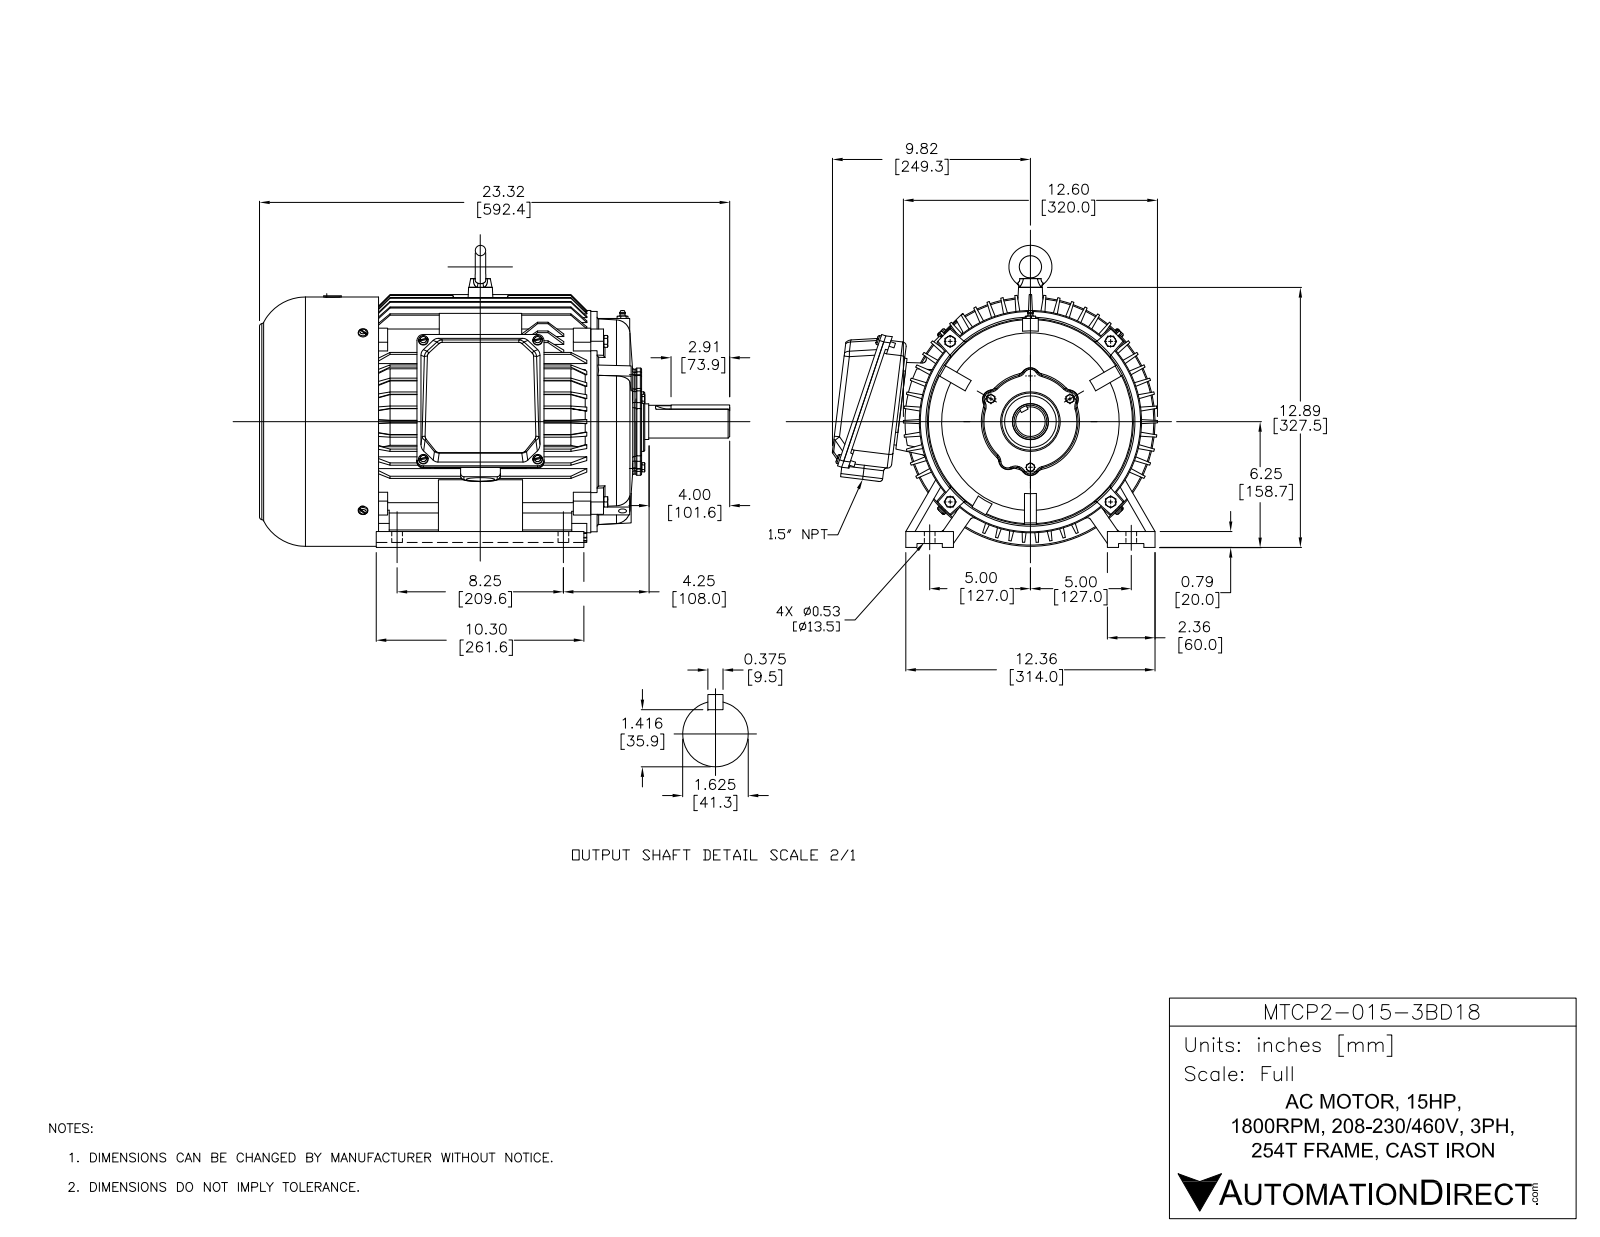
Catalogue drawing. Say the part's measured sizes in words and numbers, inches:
The part is named "PEWWE-254T". Its 3-D file was written by "SolidWorks 2017 (AUTOMOTIVE_DESIGN)". It is 28 solids with 2218 faces: 1376 planar, 420 cylindrical and 422 other. Overall it measures 23.327 by 16.126 by 14.984 inches. Its volume is 453.1 cubic inches and its surface area 3 048 square inches. Round holes: 13 of diameter 0.276, 10 of diameter 0.236, 8 of diameter 0.315, 8 of diameter 0.394, 4 of diameter 0.197, 4 of diameter 0.551, 2 of diameter 0.748, 1 of diameter 0.079, 1 of diameter 0.472, 1 of diameter 1.417, 1 of diameter 1.791, 1 of diameter 2.559. Round bosses or shafts: 8 of diameter 0.236, 1 of diameter 12.362, 1 of diameter 11.024, 1 of diameter 10.928, 1 of diameter 2.953, 1 of diameter 1.772, 1 of diameter 1.626, 1 of diameter 1.575. Partial cylindrical surfaces (rounded edges, fillets, slot ends): 48 of radius 0.394, 30 of radius 0.157, 14 of radius 0.197, 8 of radius 0.315, 7 of radius 0.138, 4 of radius 0.63, 2 of radius 0.004, 2 of radius 0.118. The main face-to-face distances are 0.197, 16.319, 0.059, 16.378, 0.787, 1.488, 17.807, 17.866, 2.52, 10.945. The hole center spacings are 2.953, 4.176, 2.264, 7.406, 3.921, 5.498, 6.589, 2.263.
